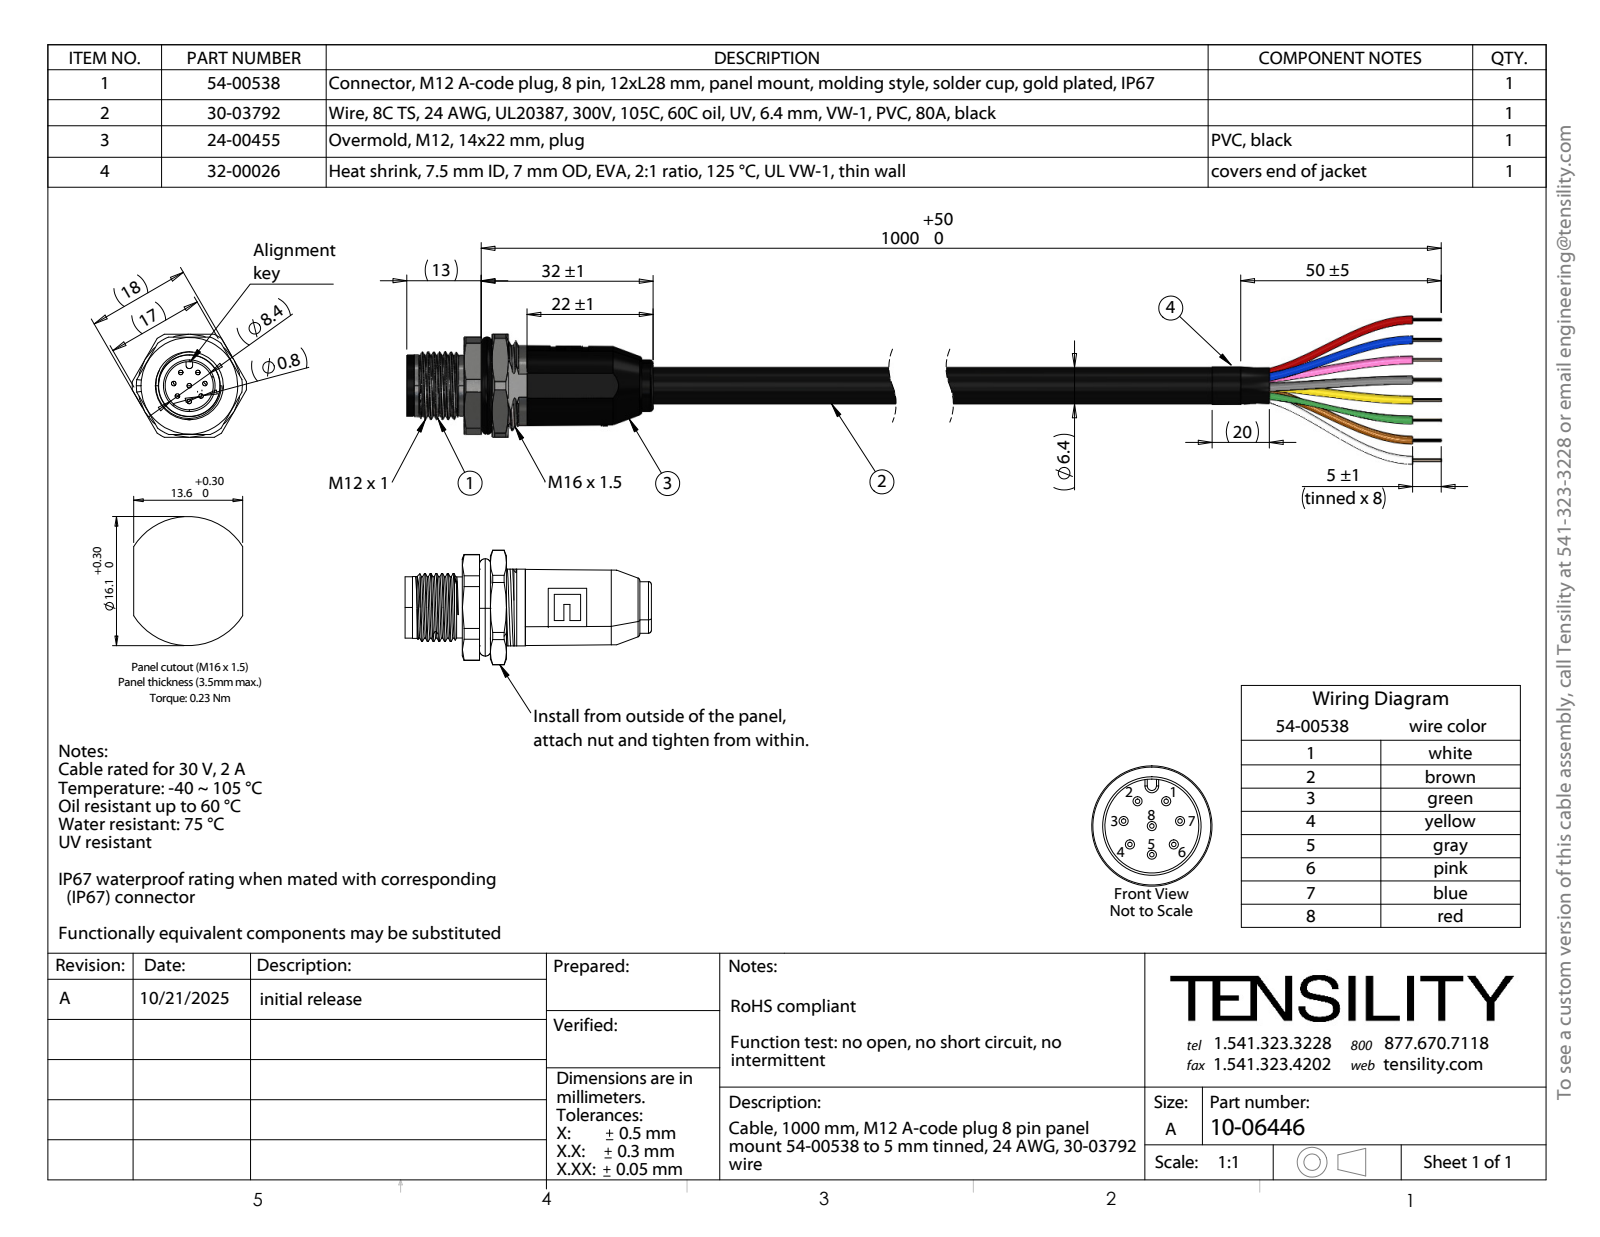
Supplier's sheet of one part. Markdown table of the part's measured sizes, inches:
| quantity | value |
| --- | --- |
| part name | 30-03792_50mm; 10-06446; 32-00026_10 mm; 54-00538 (+2 more) |
| STEP written by | SolidWorks 2025 (CONFIG_CONTROL_DESIGN) |
| units | inches |
| bodies | 327 solids, 1810 faces (779 planar, 838 cylindrical, 193 other) |
| overall size | 8.976 × 1.02 × 0.787 |
| volume | 0.655 in³ |
| surface area | 17.4 in² |
| round holes (diameter × count) | 0.038 × 8, 0.295 × 1, 0.331 × 1, 0.37 × 1, 0.378 × 1, 0.48 × 1, 0.579 × 1 |
| round bosses / shafts (diameter × count) | 0.059 × 8, 0.055 × 8, 0.031 × 8, 0.549 × 1, 0.492 × 1, 0.467 × 1, 0.433 × 1, 0.425 × 1 |
| partial cylindrical surfaces (radius × count) | 0.02 × 2, 0.108 × 1, 0.277 × 1, 0.311 × 1, 0.364 × 1, 0.394 × 1 |
| main face-to-face distances | 0.217, 0.433, 0.02, 0.374, 0.157, 0.315, 0.059, 0.689, 0.709, 0.209 |
| hole center spacings | 0.108, 0.163, 0.089, 0.09, 0.09, 0.183, 0.207, 0.208 |
